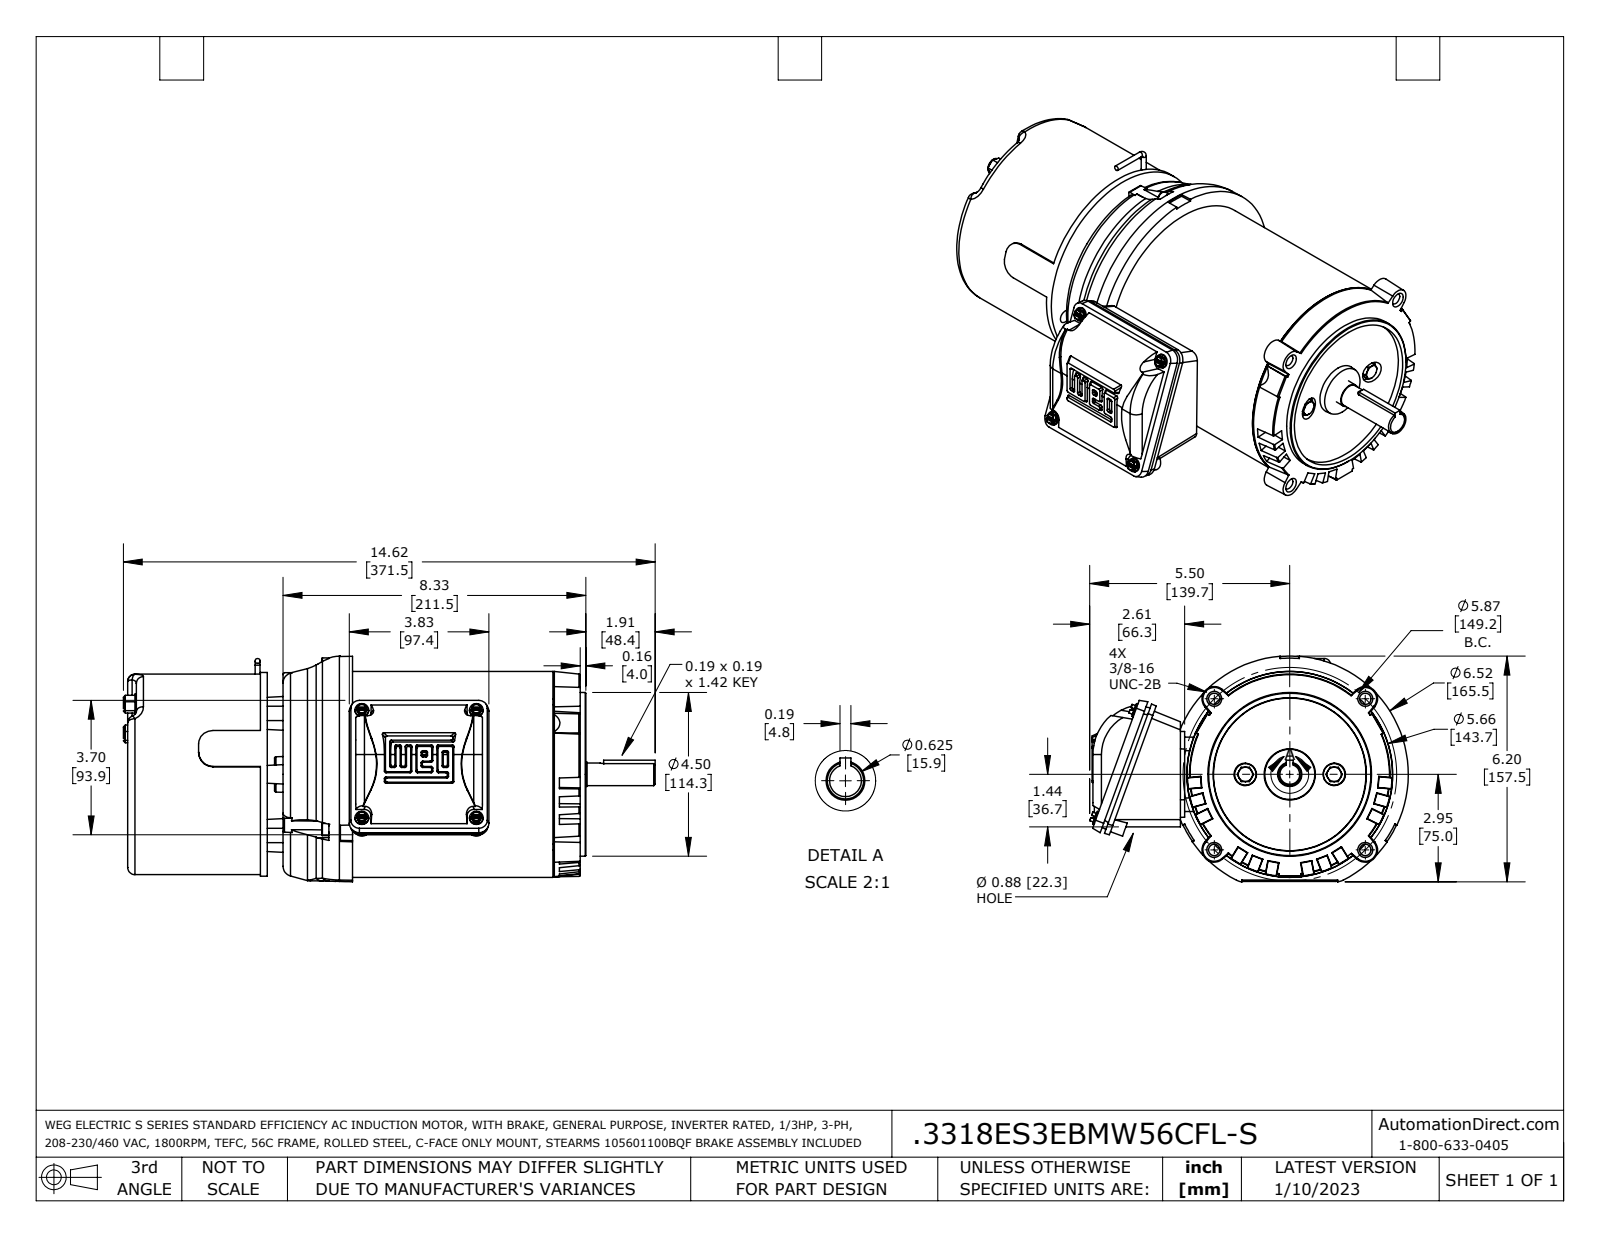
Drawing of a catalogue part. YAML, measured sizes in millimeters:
part_name: "W56C_3PH_TEFC_BM_1461_FL coord fxt"
step_written_by: "SolidWorks 2021 (AUTOMOTIVE_DESIGN)"
units: millimeters
bodies: {solids: 15, faces: 1177, planar: 471, cylindrical: 231, other: 475}
overall_size: [371.4, 222.5, 157.5]
volume: 4941000
surface_area: 411800
round_holes:
  - {diameter: 6, count: 4}
  - {diameter: 8, count: 4}
  - {diameter: 6.4, count: 2}
  - {diameter: 7.1, count: 2}
  - {diameter: 9.4, count: 2}
  - {diameter: 12.7, count: 1}
  - {diameter: 76.2, count: 1}
round_bosses_or_shafts:
  - {diameter: 9.5, count: 4}
  - {diameter: 4.7, count: 4}
  - {diameter: 8.5, count: 3}
  - {diameter: 5, count: 3}
  - {diameter: 14, count: 2}
  - {diameter: 11.1, count: 2}
  - {diameter: 3.5, count: 2}
  - {diameter: 143.7, count: 1}
partial_cylinders:
  - {radius: 1.2, count: 38}
  - {radius: 5, count: 10}
  - {radius: 5.2, count: 8}
  - {radius: 0.5, count: 4}
  - {radius: 7, count: 4}
  - {radius: 9.5, count: 4}
  - {radius: 12.2, count: 4}
  - {radius: 1, count: 3}
face_to_face_distances: [140, 14.5, 154.5, 45, 181, 26.5, 41, 18.5, 59.5, 199.5]
hole_center_spacings: [53, 74.6, 105.5, 113.4, 80, 18.2, 24.8, 37.7]
